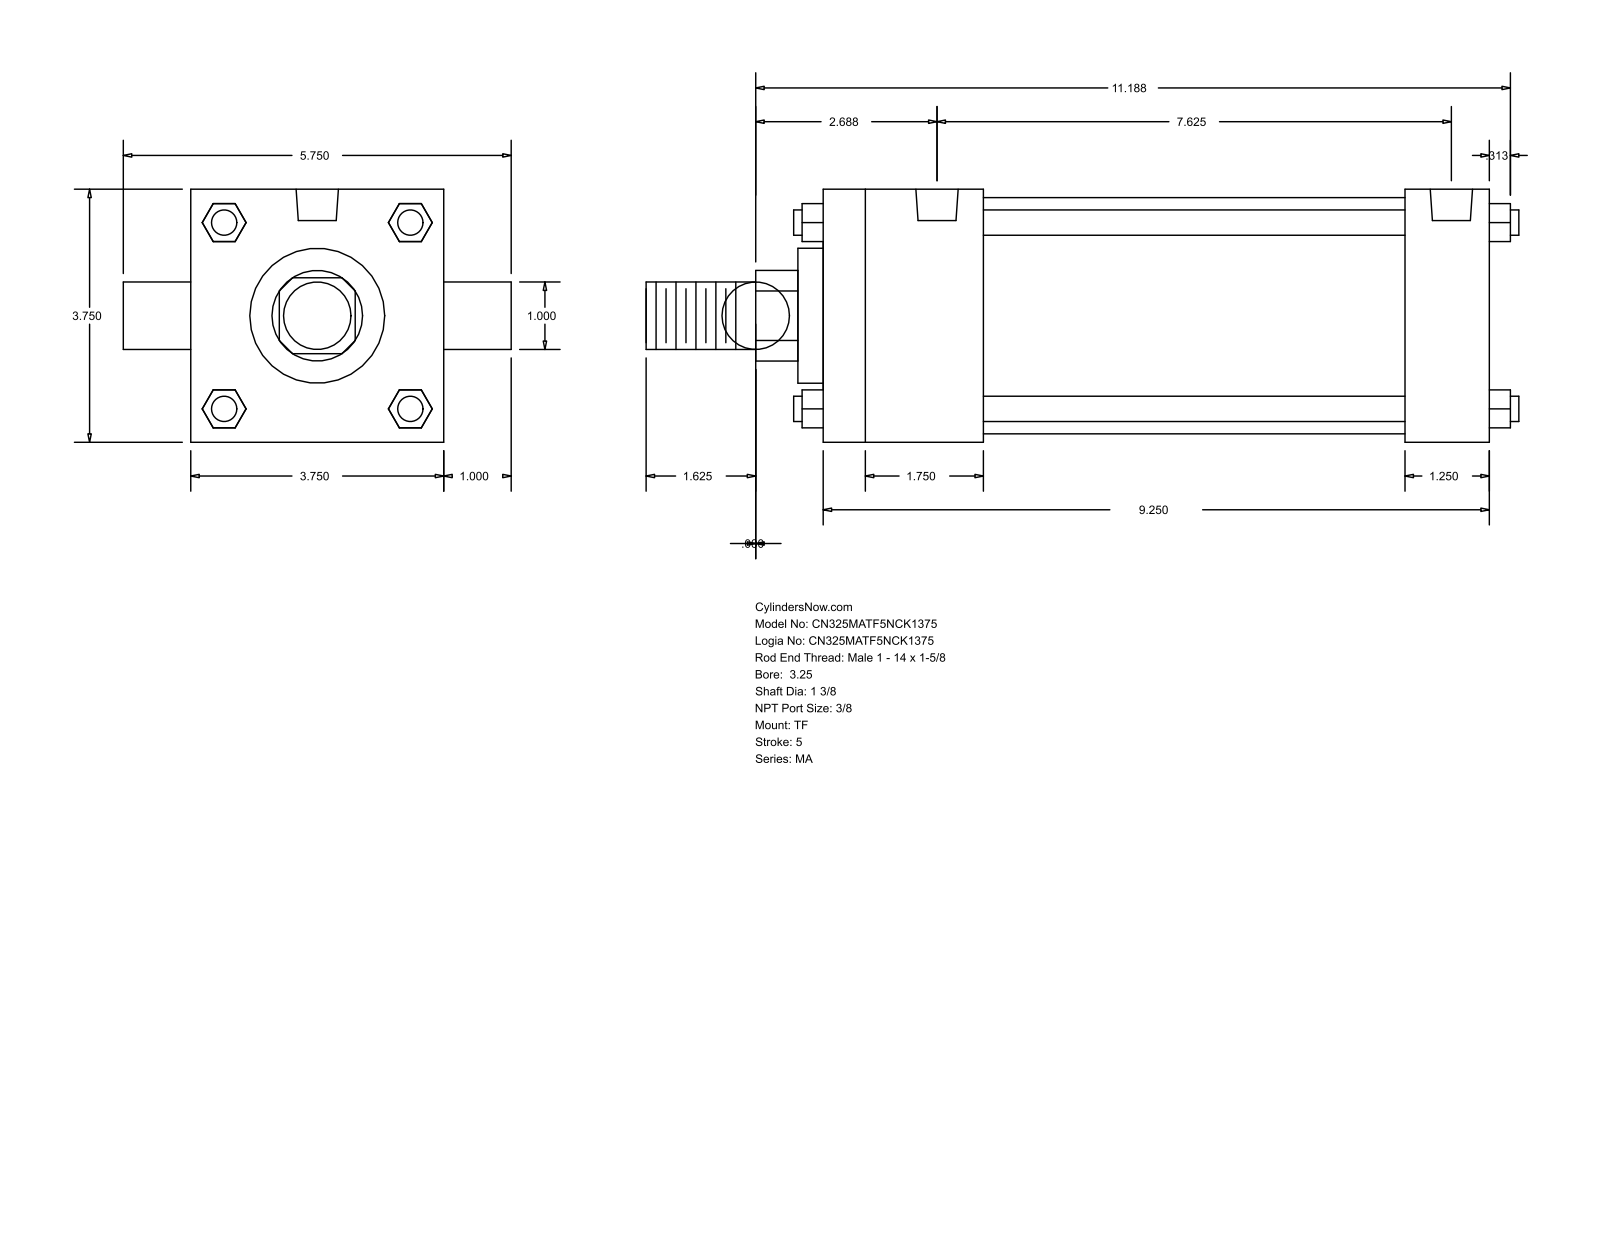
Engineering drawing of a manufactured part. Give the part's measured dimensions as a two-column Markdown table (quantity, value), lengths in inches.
| quantity | value |
| --- | --- |
| part name | MA_TF__0325_1.375 |
| STEP written by | GSSL Pune (CONFIG_CONTROL_DESIGN) |
| units | inches |
| bodies | 0 solids, 120 faces (92 planar, 28 cylindrical, 0 other) |
| overall size | 12.937 × 5.75 × 3.75 |
| round holes (diameter × count) | 0.437 × 3, 0.627 × 2 |
| round bosses / shafts (diameter × count) | 0.375 × 4, 1 × 2, 3.5 × 1, 2 × 1, 1.375 × 1 |
| partial cylindrical surfaces (radius × count) | 0.672 × 1 |
| main face-to-face distances | 3.75, 9.875, 2.375, 8.625, 6.25, 7.5, 1.25, 0.375, 2.75, 9 |
| hole center spacings | 0.187, 0.188, 7.25, 7.437, 7.438, 7.625 |
